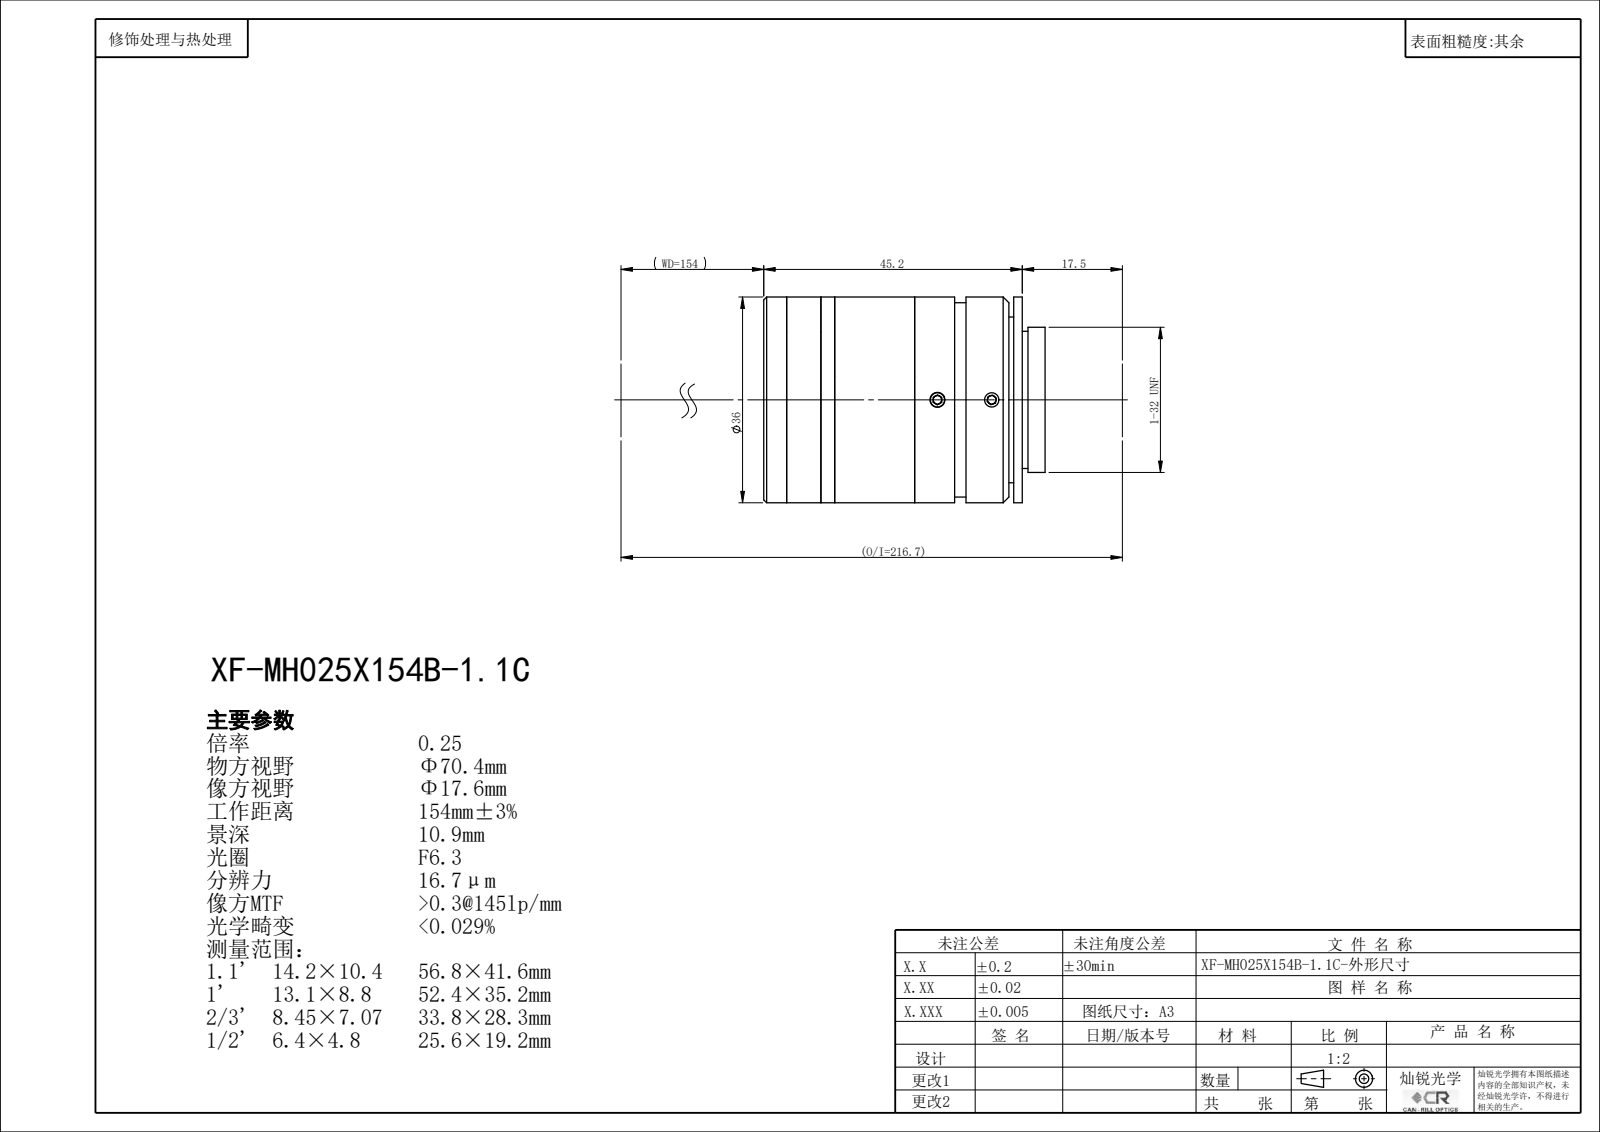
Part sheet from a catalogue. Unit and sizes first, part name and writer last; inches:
Units: inches
Overall size (bounding box): 1.939 × 1.417 × 1.417
Round holes (diameter × count): ⌀0.098 ×3, ⌀0.551 ×1, ⌀0.646 ×1, ⌀0.669 ×1, ⌀0.724 ×1, ⌀0.882 ×1, ⌀0.945 ×1, ⌀0.98 ×1, ⌀1.024 ×1
Round bosses / shafts (diameter × count): ⌀1.417 ×1, ⌀1.339 ×1, ⌀1 ×1
Main face-to-face distances: 0.742, 1.781, 1.039, 0.059, 1.722, 0.683, 1.545, 0.488, 0.551, 1.234
Bodies: 0 solids, 151 faces (77 planar, 42 cylindrical, 32 other)
Part name (STEP PRODUCT): XF-MH025X154B-1.1C
STEP written by: SolidWorks 2022 (CONFIG_CONTROL_DESIGN)
